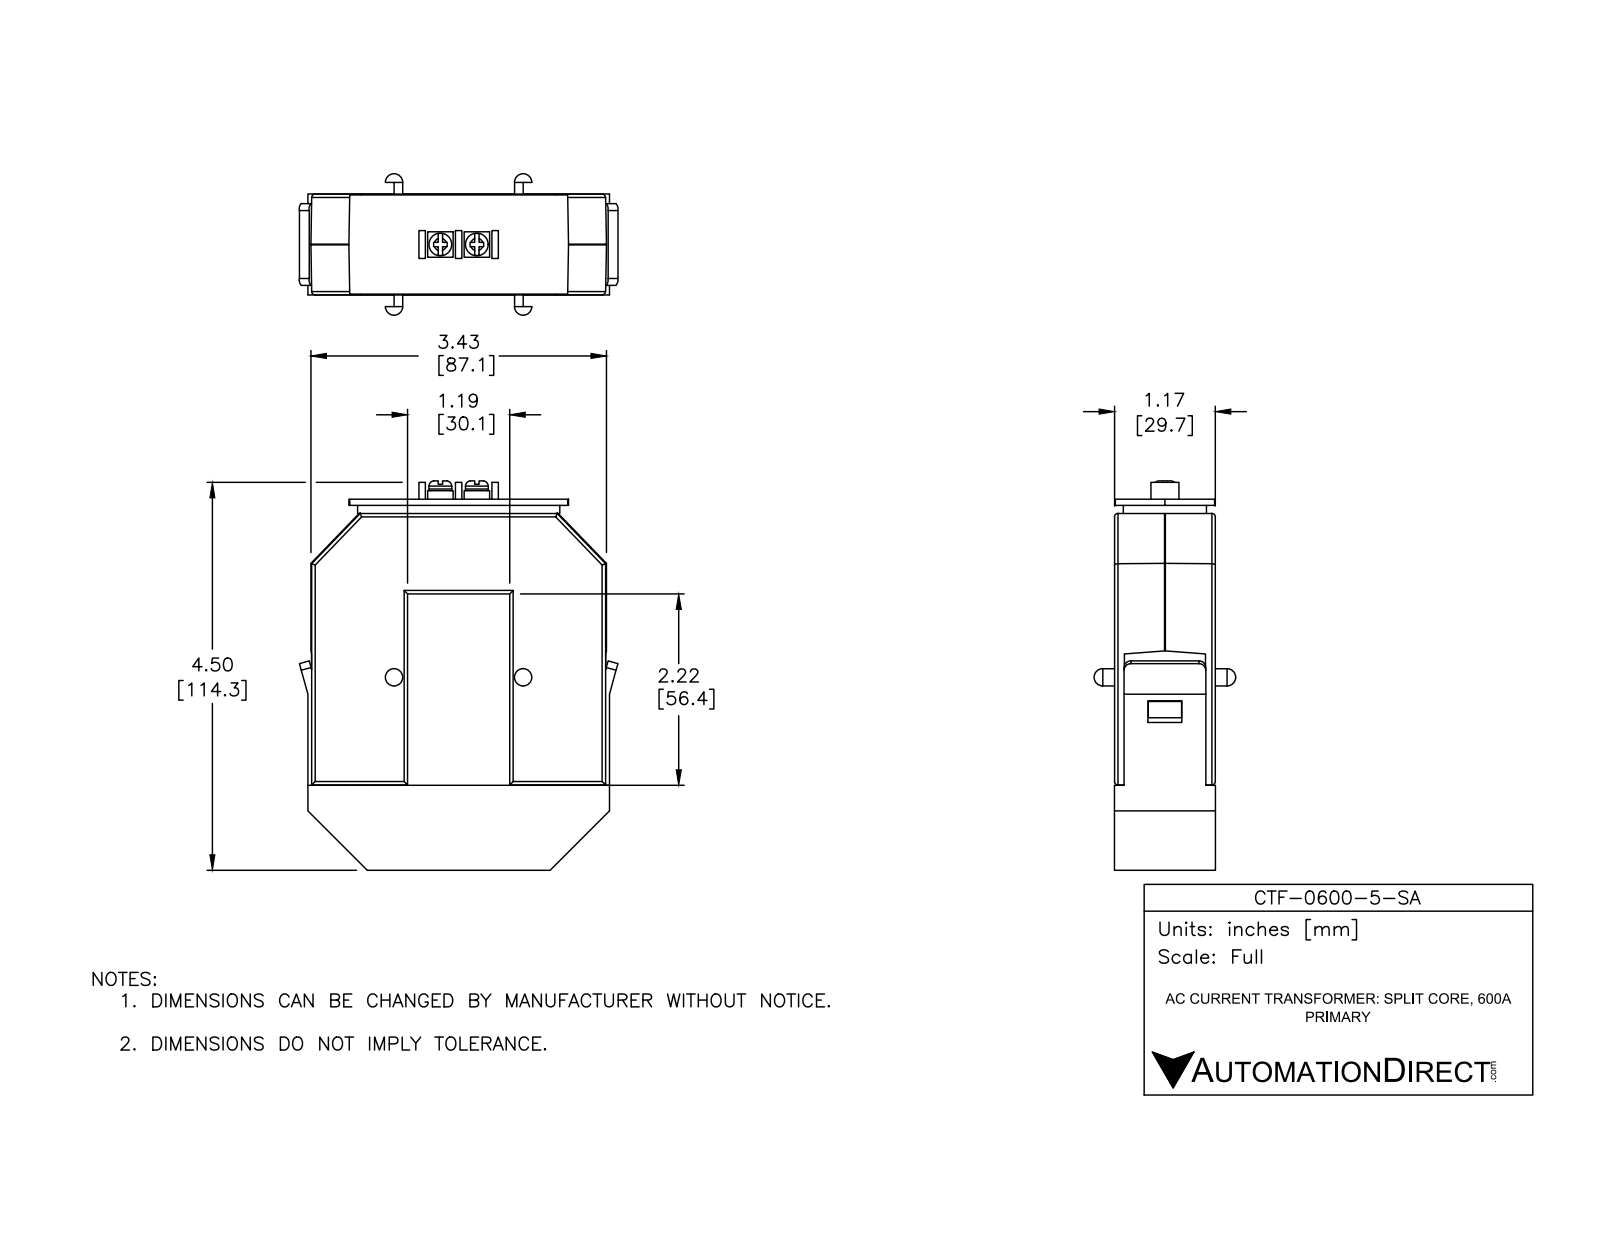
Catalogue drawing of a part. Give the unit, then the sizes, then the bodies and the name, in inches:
Units: inches
Overall size (bounding box): 4.517 × 3.696 × 1.642
Round bosses / shafts (diameter × count): ⌀0.264 ×2
Partial cylindrical surfaces — rounded edges, fillets, slot ends (radius × count): R0.04 ×18, R0.08 ×4, R0.1 ×2
Main face-to-face distances: 1.169, 1.17, 2.22, 3.319, 1.172, 0.118, 1.157, 2.342, 0.986, 4.305
Volume: 13.27 in³ · Surface area: 62.61 in²
Bodies: 8 solids, 210 faces (160 planar, 34 cylindrical, 16 other)
Part name (STEP PRODUCT): CTF-0600-5-SA
STEP written by: SolidWorks 2016 (AUTOMOTIVE_DESIGN)
